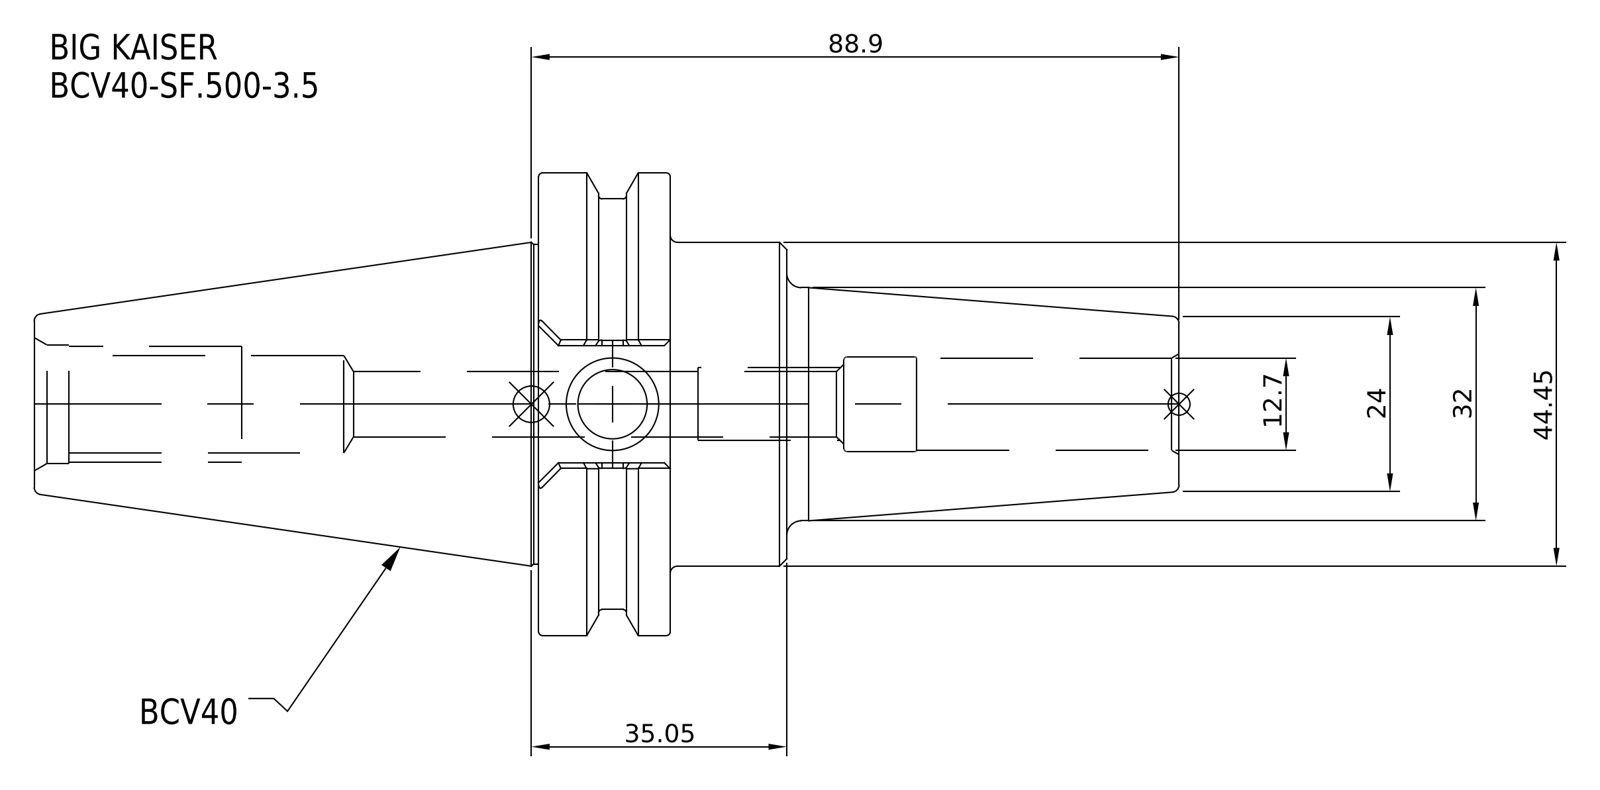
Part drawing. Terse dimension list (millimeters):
name: BCV40-SF_500-3_5
written by: SolidWorks 2021 (CONFIG_CONTROL_DESIGN)
unit: mm
bodies: 1 solid, 30 faces (8 planar, 14 cylindrical, 8 other)
size: 157.15 × 63.5 × 63.5
volume: 175 038 mm³; area: 25 361 mm²
holes: 1× ⌀12.7
bosses: 1× ⌀63.5, 1× ⌀56.36, 1× ⌀44.45, 1× ⌀32
face distances: 18.05, 16, 34.05, 103.3, 87.3, 69.25, 53.85, 69.85, 87.9, 157.15
